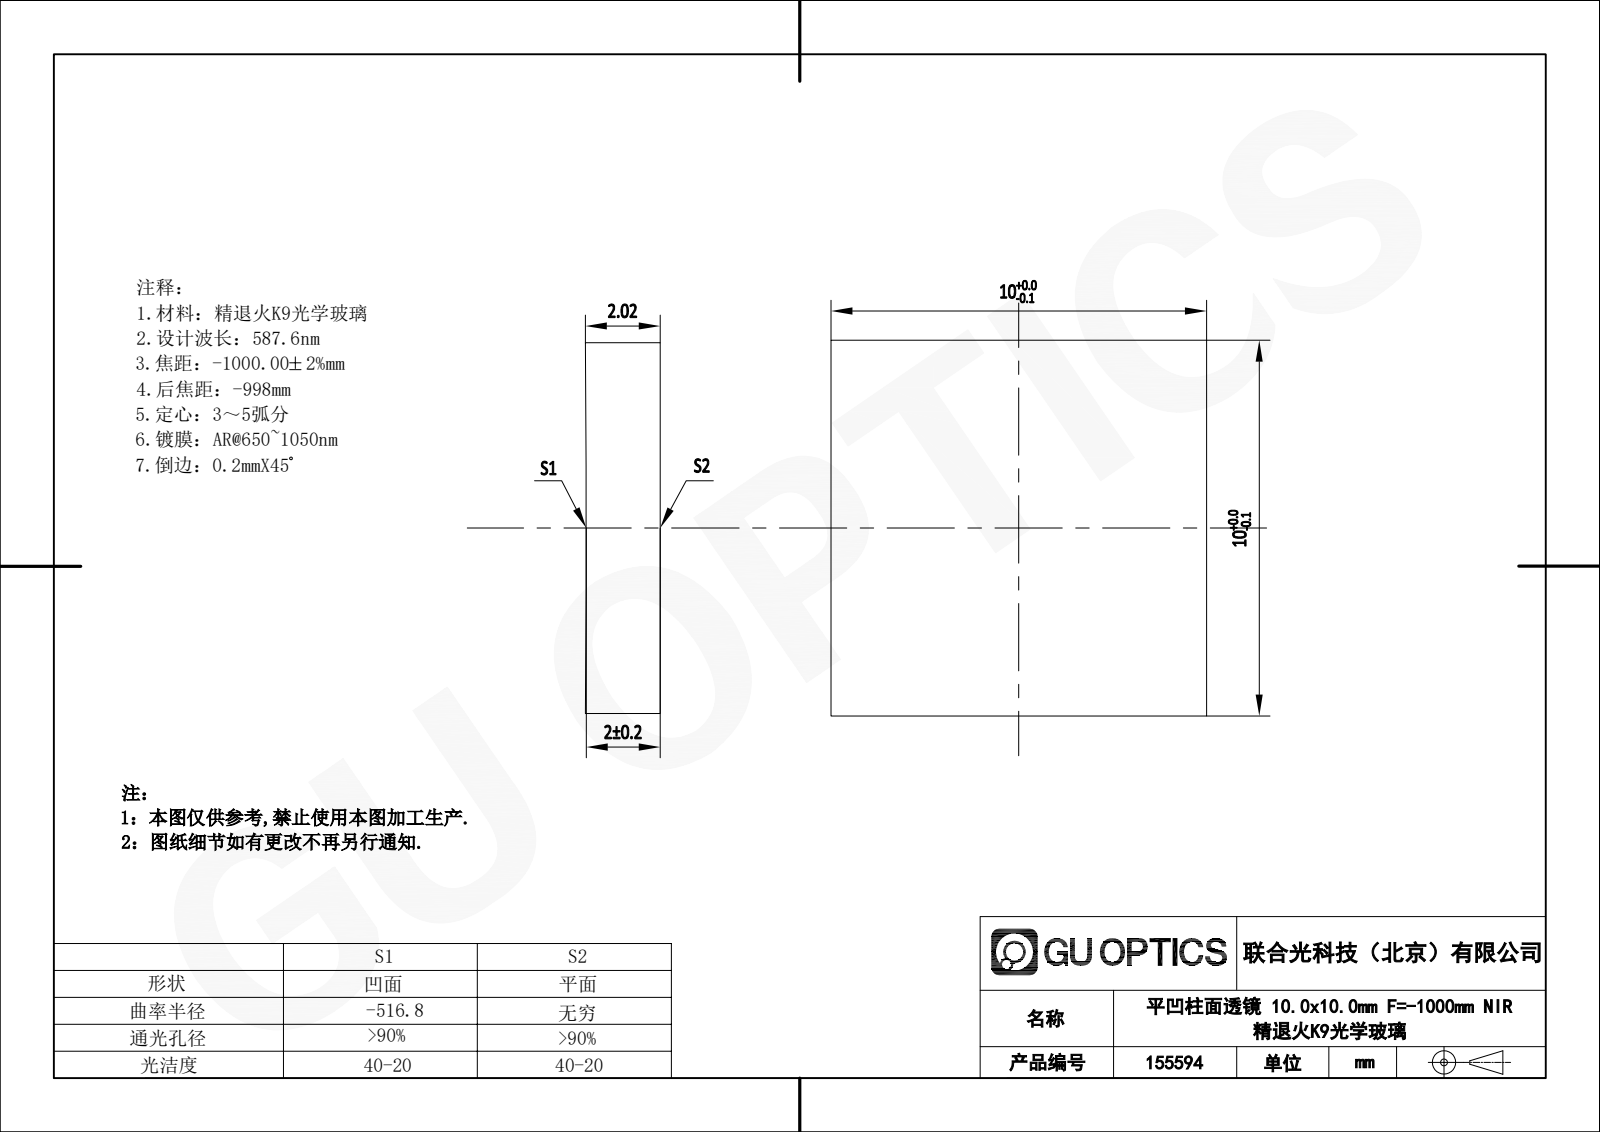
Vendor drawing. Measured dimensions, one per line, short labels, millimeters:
name: 155574
written by: SolidWorks 2020 (CONFIG_CONTROL_DESIGN)
unit: mm
bodies: 1 solid, 6 faces (5 planar, 1 cylindrical, 0 other)
size: 10 × 10 × 2.02
volume: 200 mm³; area: 280 mm²
rounds: 1× R516.8
face distances: 10
